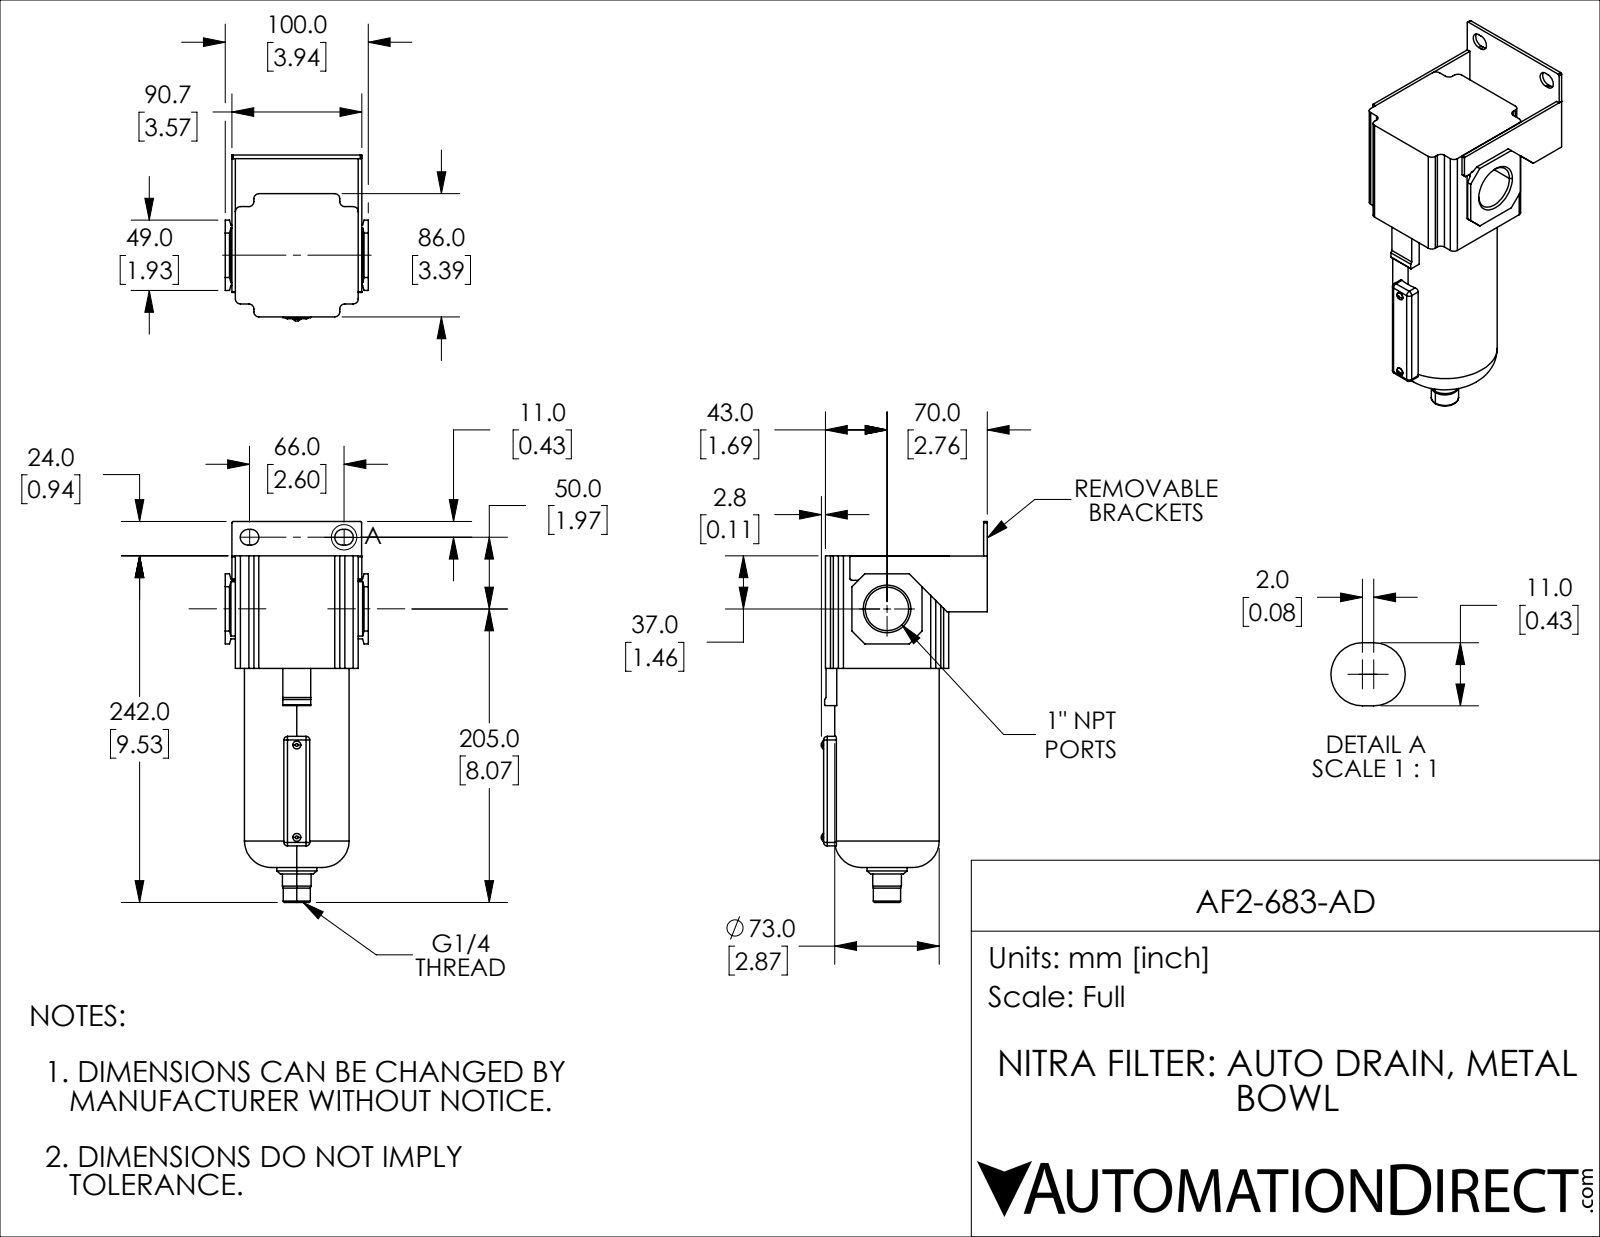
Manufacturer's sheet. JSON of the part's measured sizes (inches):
{"part_name": "AF2-683-AD", "step_written_by": "SolidWorks 2019 (CONFIG_CONTROL_DESIGN)", "units": "inches", "bodies": {"solids": 1, "faces": 160, "planar": 94, "cylindrical": 44, "other": 22}, "overall_size": [10.472, 4.559, 3.937], "volume_in3": 69.38, "surface_area_in2": 156.3, "round_holes": [[0.337, 1], [1.193, 1]], "round_bosses_or_shafts": [[0.217, 2], [2.874, 1], [1.102, 1], [0.787, 1], [0.748, 1]], "partial_cylinders_radius": [[0.138, 12], [0.098, 8], [0.217, 4], [0.039, 2]], "face_to_face_distances": [0.098, 3.472, 0.965, 4.449, 3.386, 1.063, 4.35, 3.374, 0.183, 0.281]}
